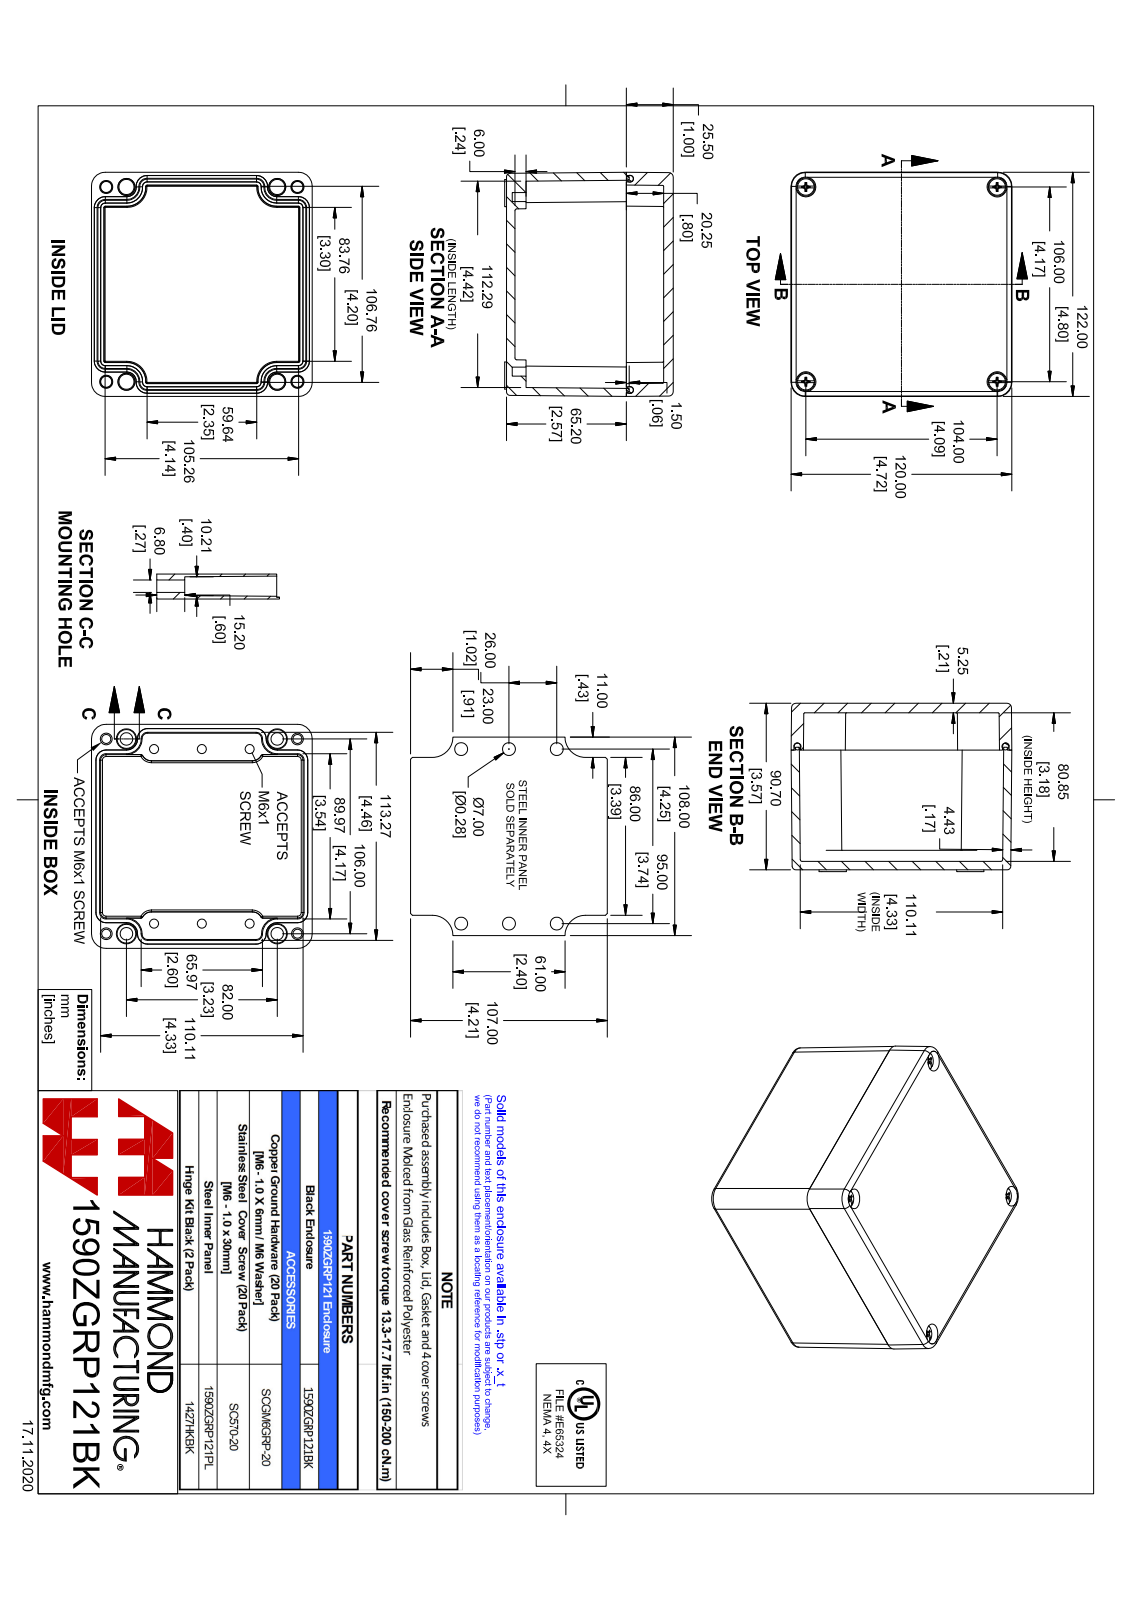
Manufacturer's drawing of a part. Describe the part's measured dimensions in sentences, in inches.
The part is named "1590ZGRP121BK". Its 3-D file was written by "SolidWorks 2021 (AUTOMOTIVE_DESIGN)". It is 8 solids with 517 faces: 229 planar, 108 cylindrical and 180 other. Overall it measures 4.803 by 4.724 by 3.61 inches. Its volume is 24.44 cubic inches and its surface area 276.4 square inches. Round holes: 10 of diameter 0.194, 6 of diameter 0.276, 4 of diameter 0.236, 4 of diameter 0.252, 4 of diameter 0.268, 4 of diameter 0.425. Round bosses or shafts: 6 of diameter 0.148, 4 of diameter 0.231, 4 of diameter 0.208. Partial cylindrical surfaces (rounded edges, fillets, slot ends): 20 of radius 0.059, 6 of radius 0.02, 6 of radius 0.039, 4 of radius 0.079, 4 of radius 0.098, 4 of radius 0.295, 4 of radius 0.315, 4 of radius 0.433. The main face-to-face distances are 3.571, 0.417, 3.154, 0.207, 0.02, 0.437, 3.134, 3.364, 2.947, 2.927. The hole center spacings are 0.433, 0.629, 1.024, 1.046, 1.629, 2.059, 2.647, 3.078.
